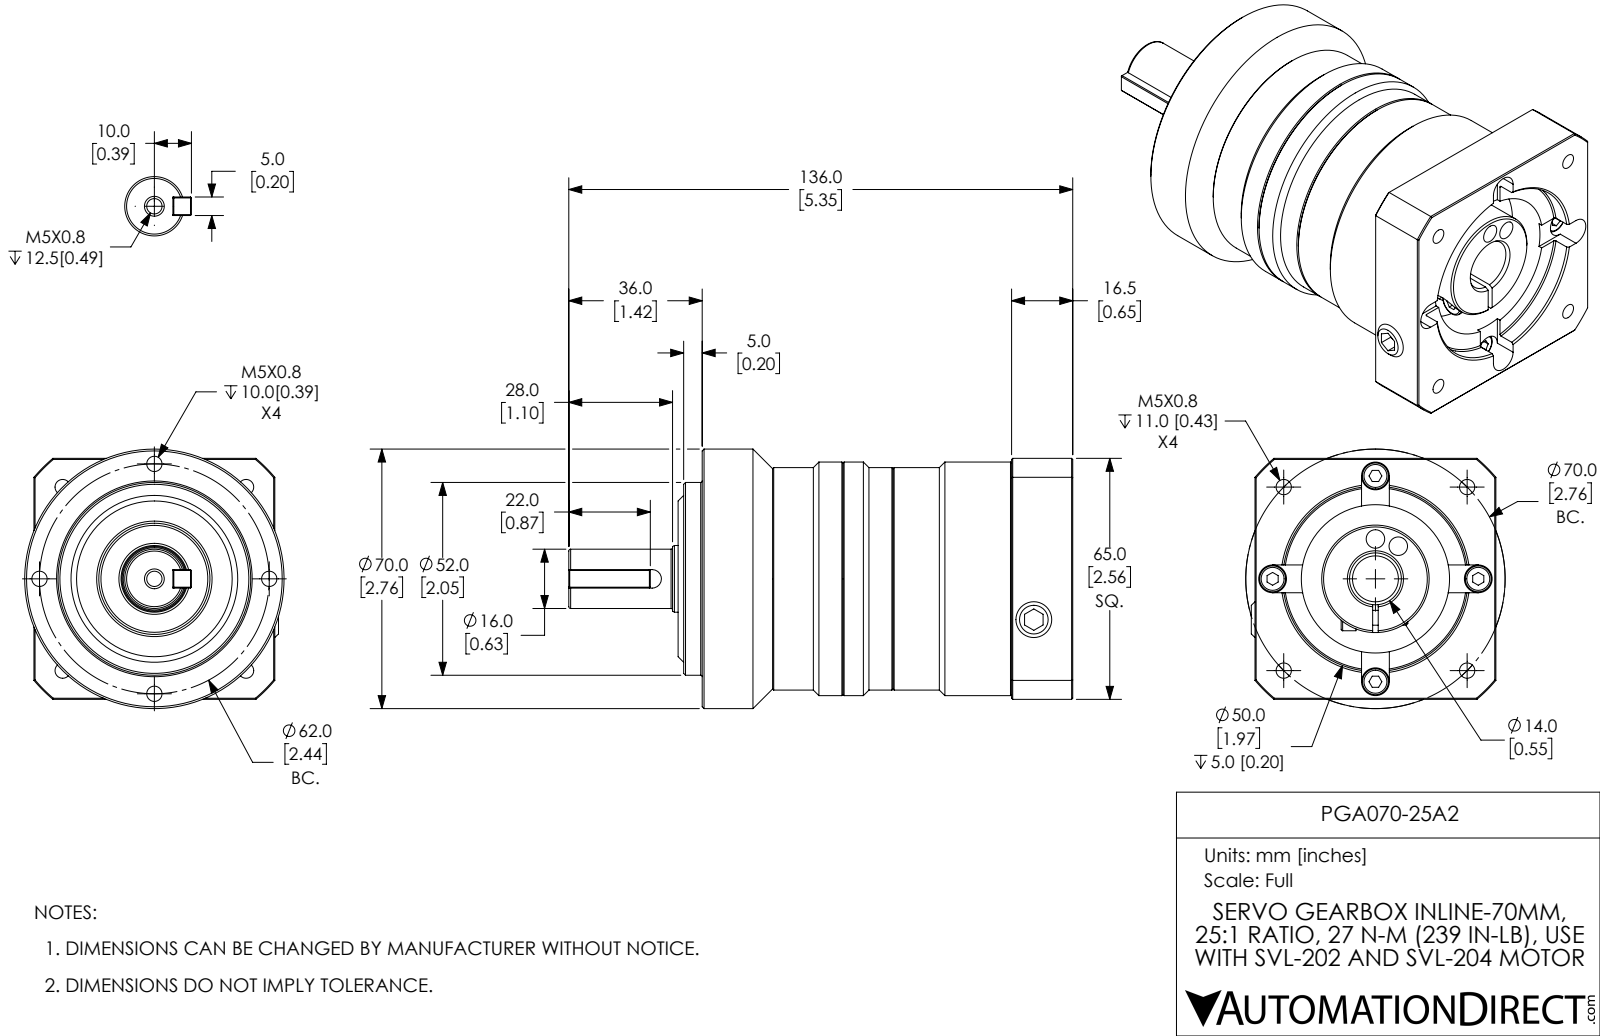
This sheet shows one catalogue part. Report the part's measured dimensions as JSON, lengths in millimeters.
{"part_name": "PGA070-25A2", "step_written_by": "SolidWorks 2019 (CONFIG_CONTROL_DESIGN)", "units": "millimeters", "bodies": {"solids": 1, "faces": 324, "planar": 127, "cylindrical": 87, "other": 110}, "overall_size": [136, 70, 70], "volume_mm3": 323476, "surface_area_mm2": 42114, "round_holes": [[4.13, 9], [7.5, 4], [5, 2], [4.5, 1], [8, 1], [14, 1], [29, 1], [40, 1], [50, 1]], "round_bosses_or_shafts": [[7, 5], [70, 1], [63, 1], [60, 1], [52, 1], [18, 1], [16, 1], [4, 1]], "partial_cylinders_radius": [[1.62, 1], [2.5, 1], [4, 1], [42.5, 1]], "face_to_face_distances": [100, 65, 16.5, 83.5, 5, 11.5, 6.5, 106.5, 90, 1.5], "hole_center_spacings": [24.93, 25.53, 41.61, 58.04, 61, 3.25, 27.75, 31]}
